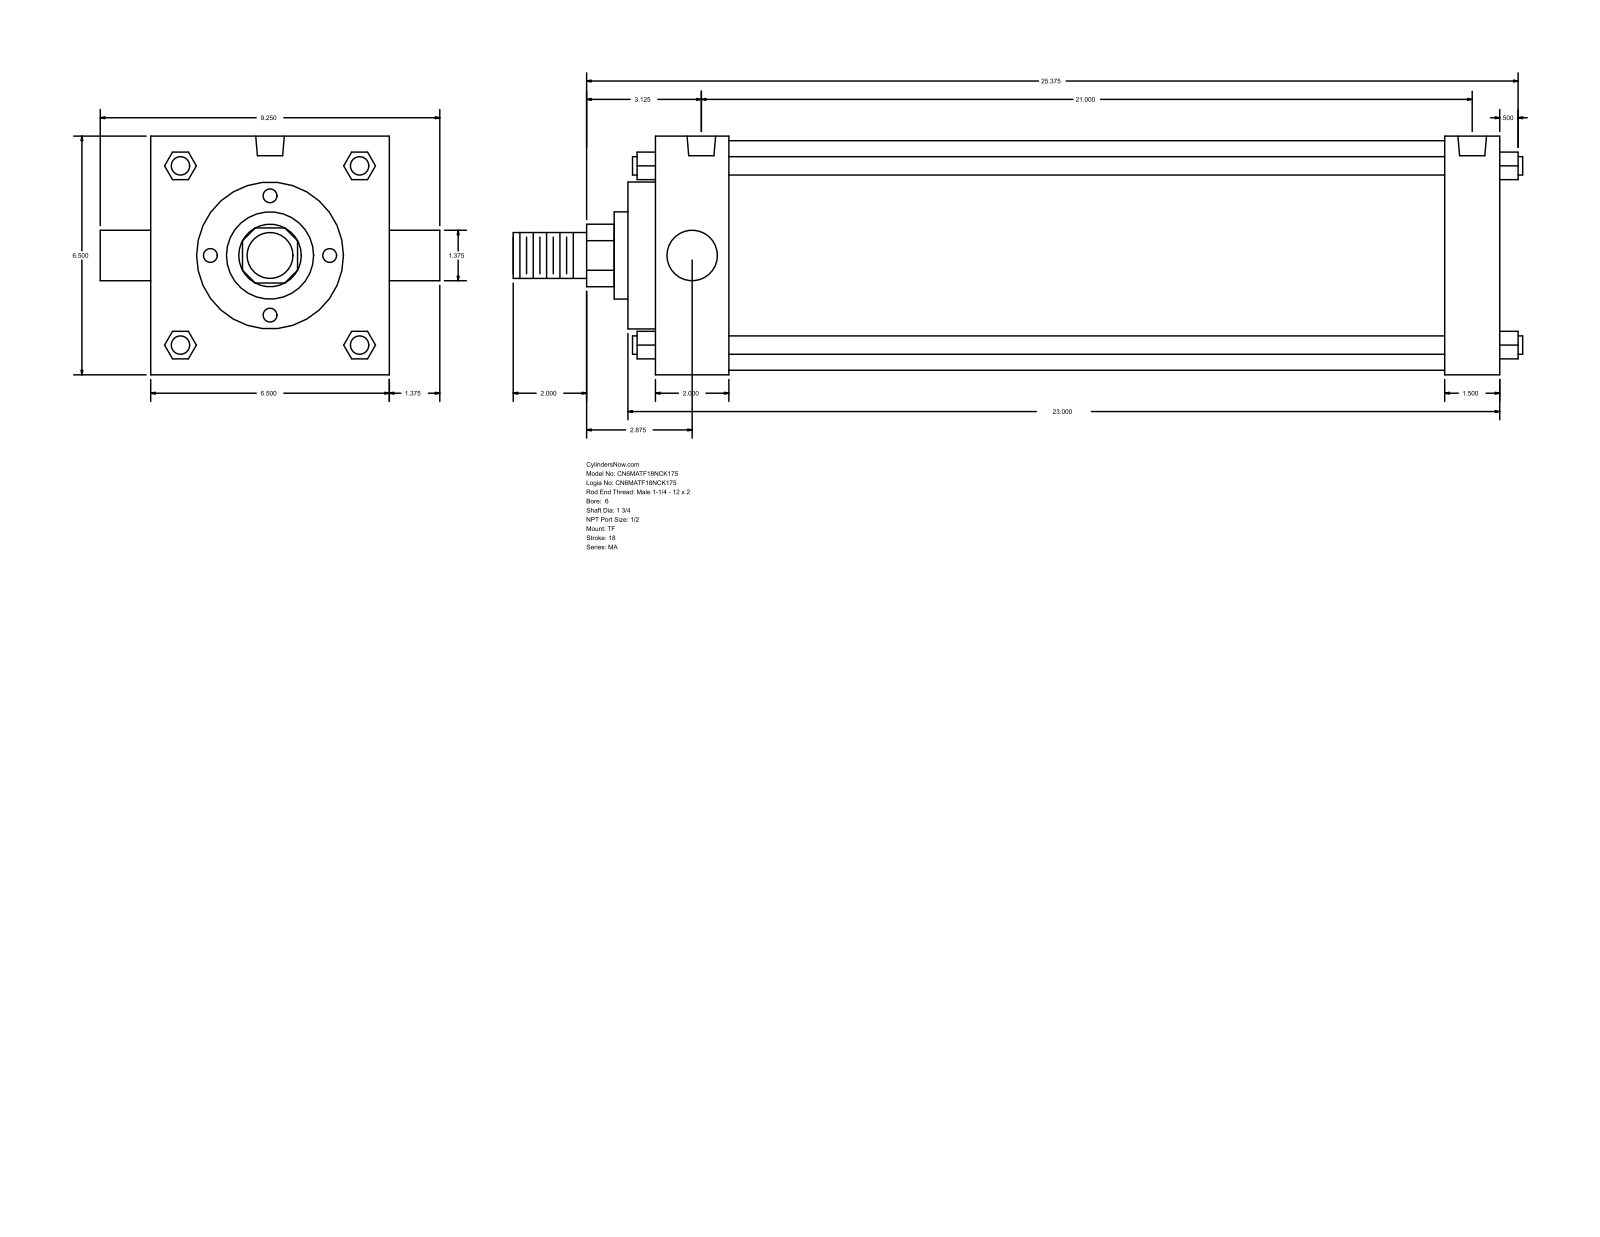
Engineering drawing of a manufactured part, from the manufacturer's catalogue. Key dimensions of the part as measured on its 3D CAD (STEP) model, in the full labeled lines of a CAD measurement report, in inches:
Part name (STEP PRODUCT): MA_TF__0600_1.75
STEP written by: GSSL Pune (CONFIG_CONTROL_DESIGN)
Units: inches
Bodies: 0 solids, 122 faces (93 planar, 29 cylindrical, 0 other)
Overall size (bounding box): 27.5 × 9.25 × 6.5
Round holes (diameter × count): ⌀0.687 ×3, ⌀0.778 ×2
Round bosses / shafts (diameter × count): ⌀0.5 ×4, ⌀6.25 ×1, ⌀4 ×1, ⌀2.375 ×1, ⌀1.75 ×1, ⌀1.375 ×1, ⌀1.25 ×1
Partial cylindrical surfaces — rounded edges, fillets, slot ends (radius × count): R0.852 ×1
Main face-to-face distances: 6.5, 23, 0.75, 1.5, 2, 21, 21.5, 19.5, 2.75, 22.25
Hole centre spacings: 21
